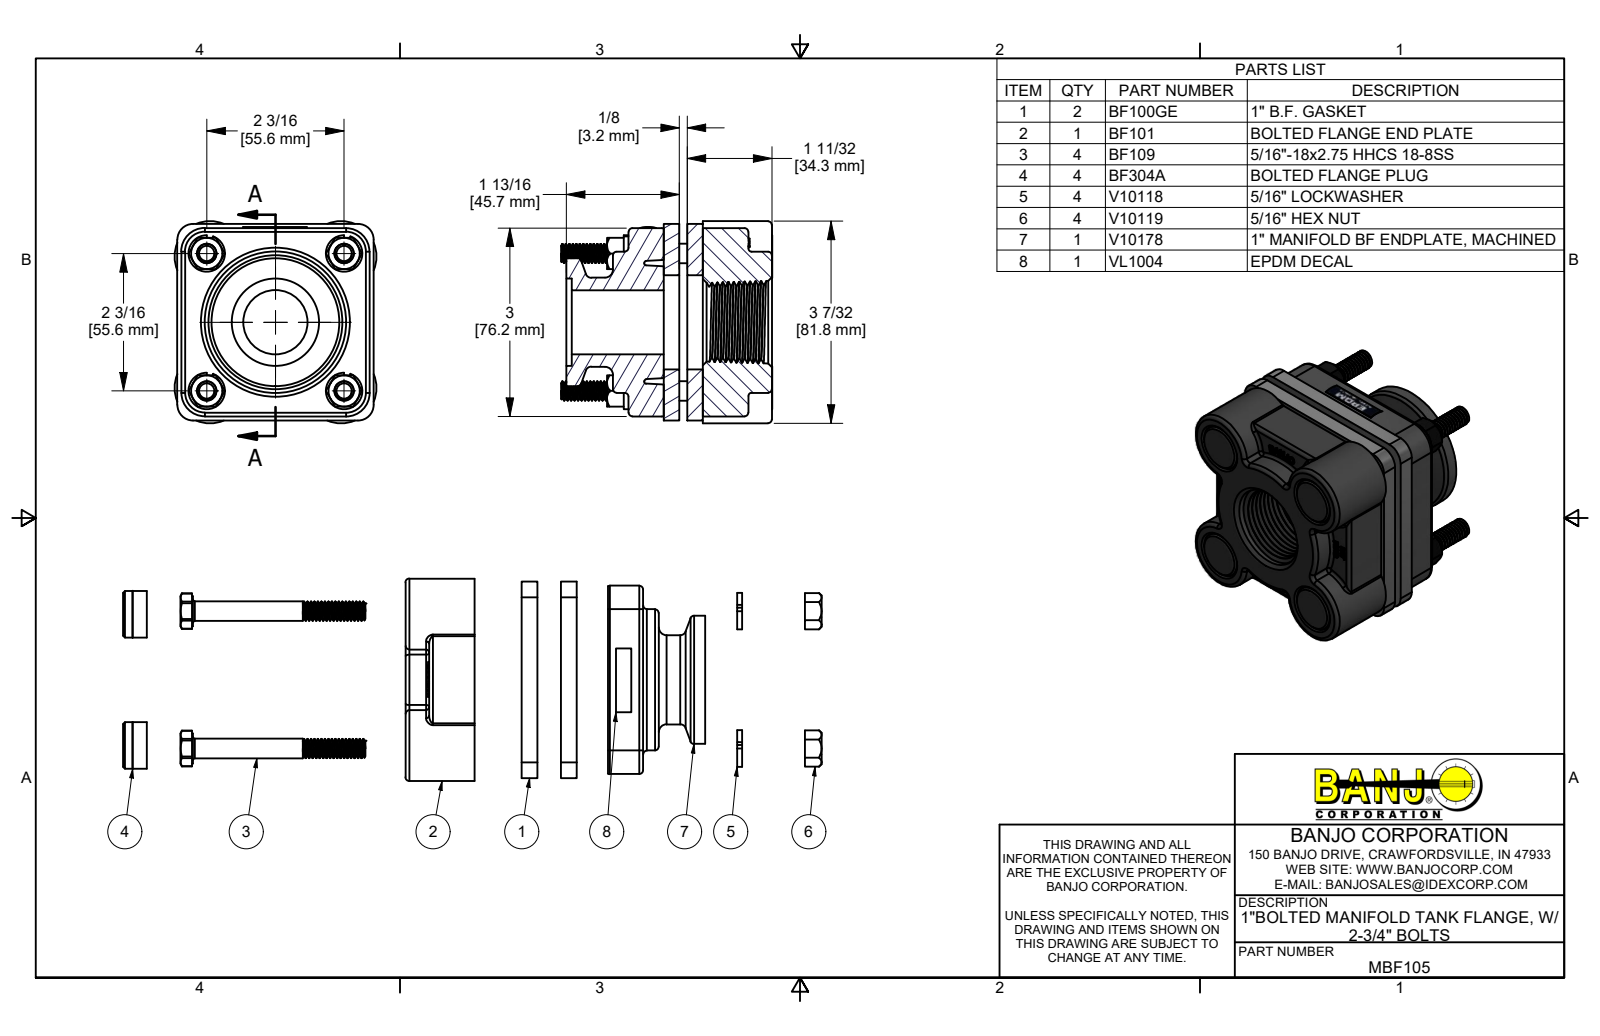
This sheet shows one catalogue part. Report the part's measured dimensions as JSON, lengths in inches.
{"part_name": "MBF105; BF101; BF109; BF304AT (+7 more)", "step_written_by": "Autodesk Inventor 2018 (AUTOMOTIVE_DESIGN)", "units": "inches", "bodies": {"solids": 21, "faces": 1146, "planar": 447, "cylindrical": 360, "other": 339}, "overall_size": [3.363, 3.22, 3.22], "volume_in3": 18.78, "surface_area_in2": 153.4, "round_holes": [[0.252, 4], [0.313, 4], [0.322, 4], [0.34, 4], [0.344, 4], [0.35, 4], [0.72, 4], [0.745, 4], [1.02, 1], [1.39, 1], [1.5, 1]], "round_bosses_or_shafts": [[0.742, 4], [0.583, 4], [0.48, 4], [0.305, 4], [0.245, 4], [2.25, 1], [2.04, 1], [1.42, 1]], "partial_cylinders_radius": [[0.03, 24], [0.06, 20], [0.05, 8], [0.062, 4], [0.25, 4], [0.375, 4], [0.565, 4], [0.375, 1]], "face_to_face_distances": [0.375, 0.25, 0.125, 0.625, 0.375, 0.625, 0.25, 1.35, 1.1, 1.185], "hole_center_spacings": [2.139, 2.146, 2.194, 0.07, 0.078, 1.478, 1.547, 1.556]}
